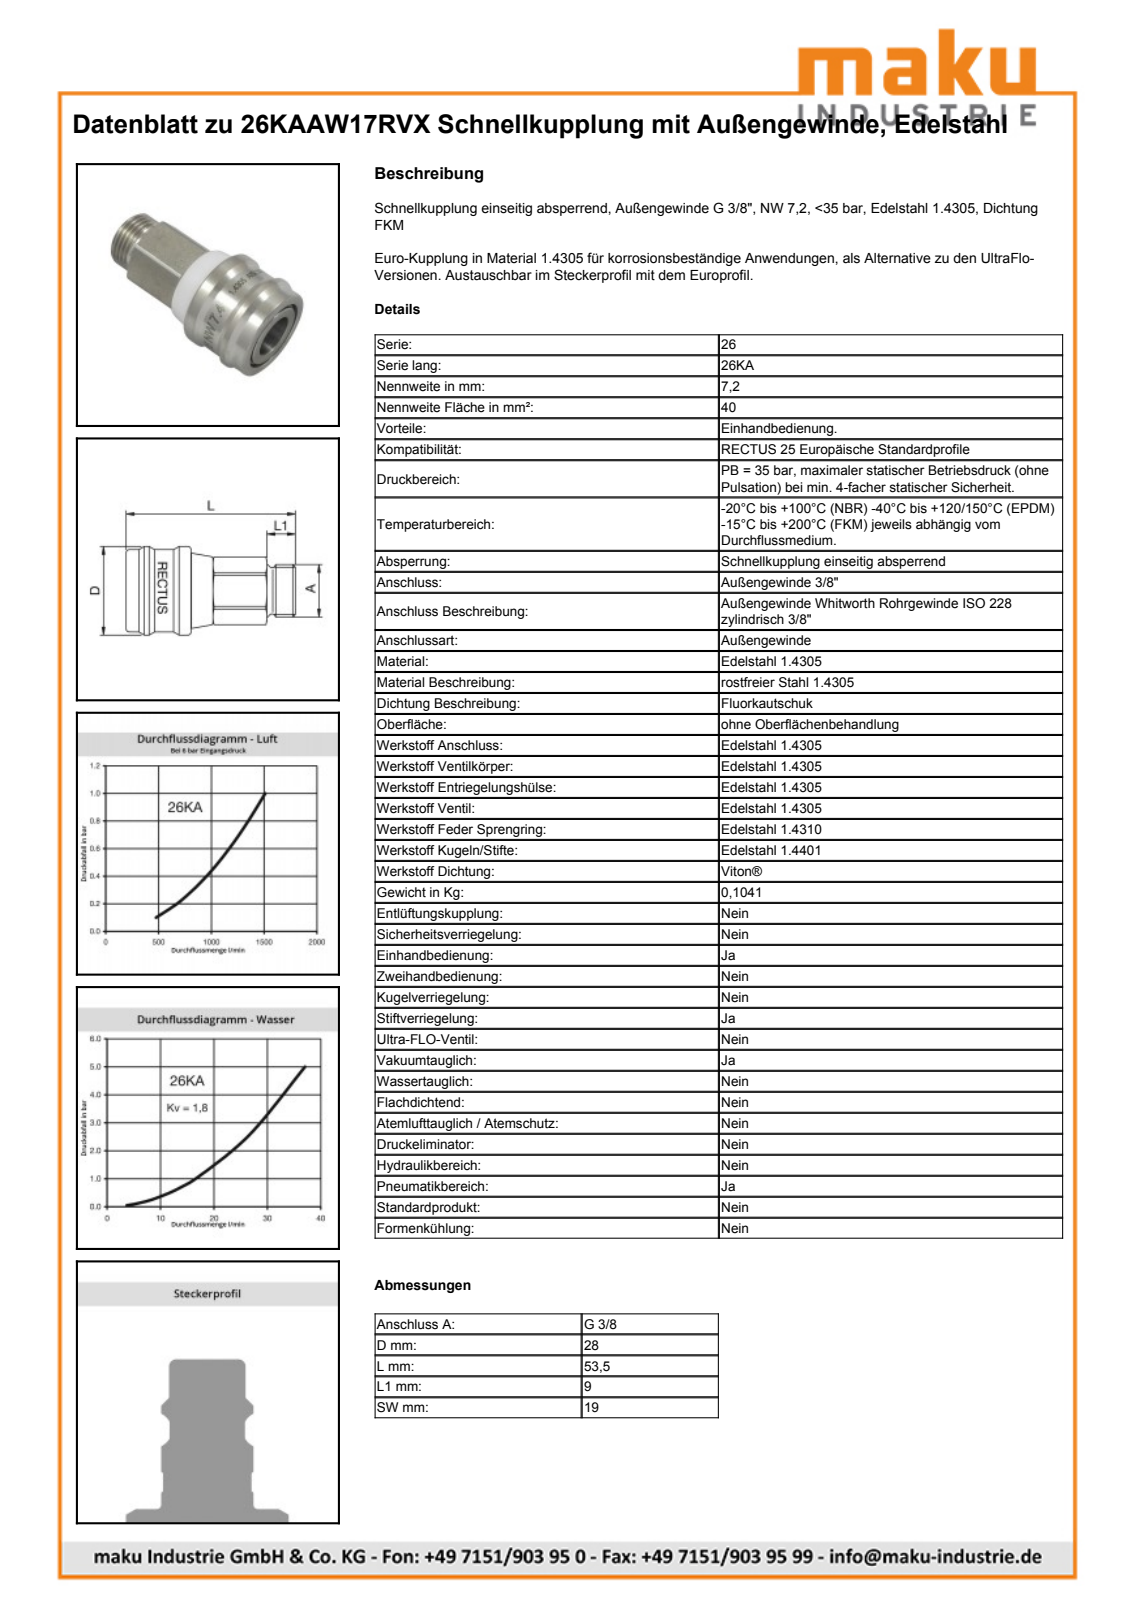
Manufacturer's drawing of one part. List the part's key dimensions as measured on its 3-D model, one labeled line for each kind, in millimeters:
Part name (STEP PRODUCT): D106057
STEP written by: Autodesk Inventor 2011 (AUTOMOTIVE_DESIGN)
Units: millimetres
Bodies: 2 solids, 563 faces (217 planar, 75 cylindrical, 271 other)
Overall size (bounding box): 53.41 × 28 × 28
Volume: 18 679 mm³ · Surface area: 9 083 mm²
Round holes (diameter × count): ⌀19.15 ×1, ⌀20 ×1, ⌀21.2 ×1, ⌀24 ×1
Round bosses / shafts (diameter × count): ⌀28 ×1, ⌀26 ×1, ⌀23.8 ×1, ⌀21 ×1, ⌀18.95 ×1, ⌀18 ×1, ⌀16.66 ×1, ⌀16.65 ×1
Partial cylindrical surfaces — rounded edges, fillets, slot ends (radius × count): R8.25 ×1, R10.7 ×1, R12.9 ×1
Main face-to-face distances: 19, 5.99, 53.4, 47.41, 6, 53.41, 20.5, 18.51, 18.5, 12.51
